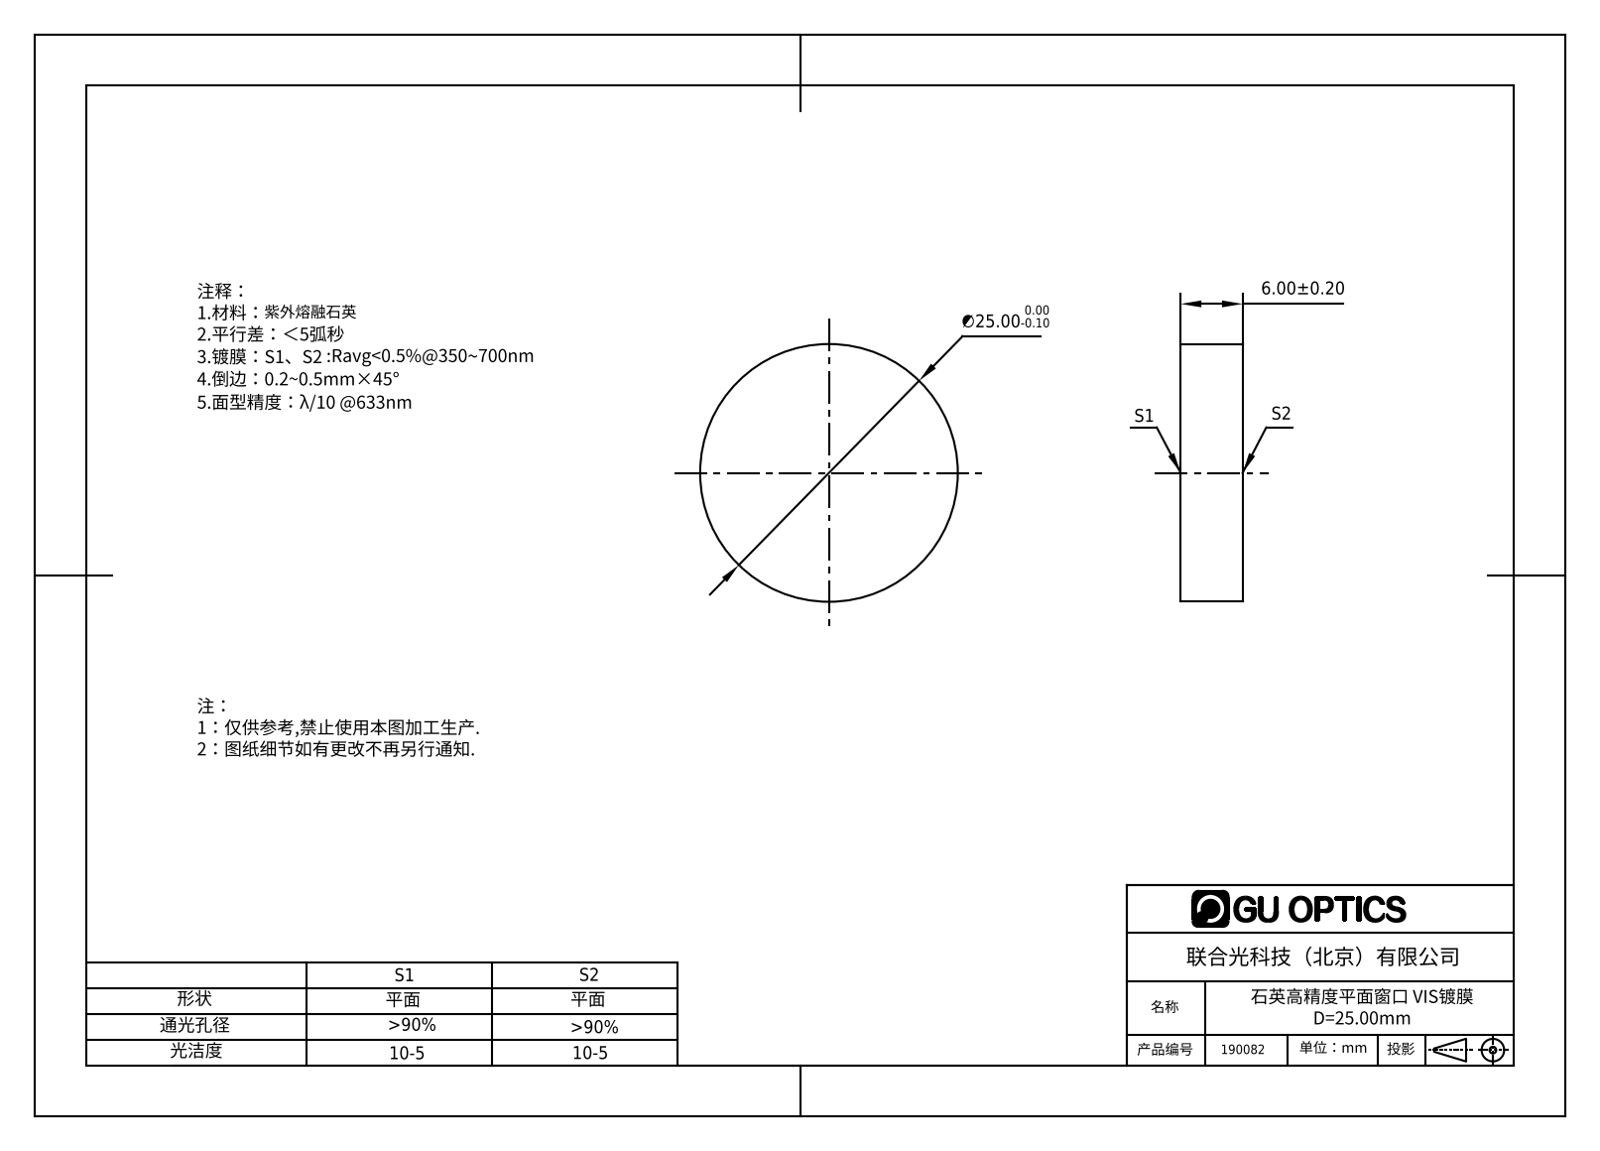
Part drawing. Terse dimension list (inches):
name: 190060
written by: SolidWorks 2016 (AUTOMOTIVE_DESIGN)
unit: in
bodies: 1 solid, 4 faces (2 planar, 2 cylindrical, 0 other)
size: 0.984 × 0.984 × 0.236
volume: 0.18 in³; area: 2.252 in²
bosses: 1× ⌀0.984
face distances: 0.236
